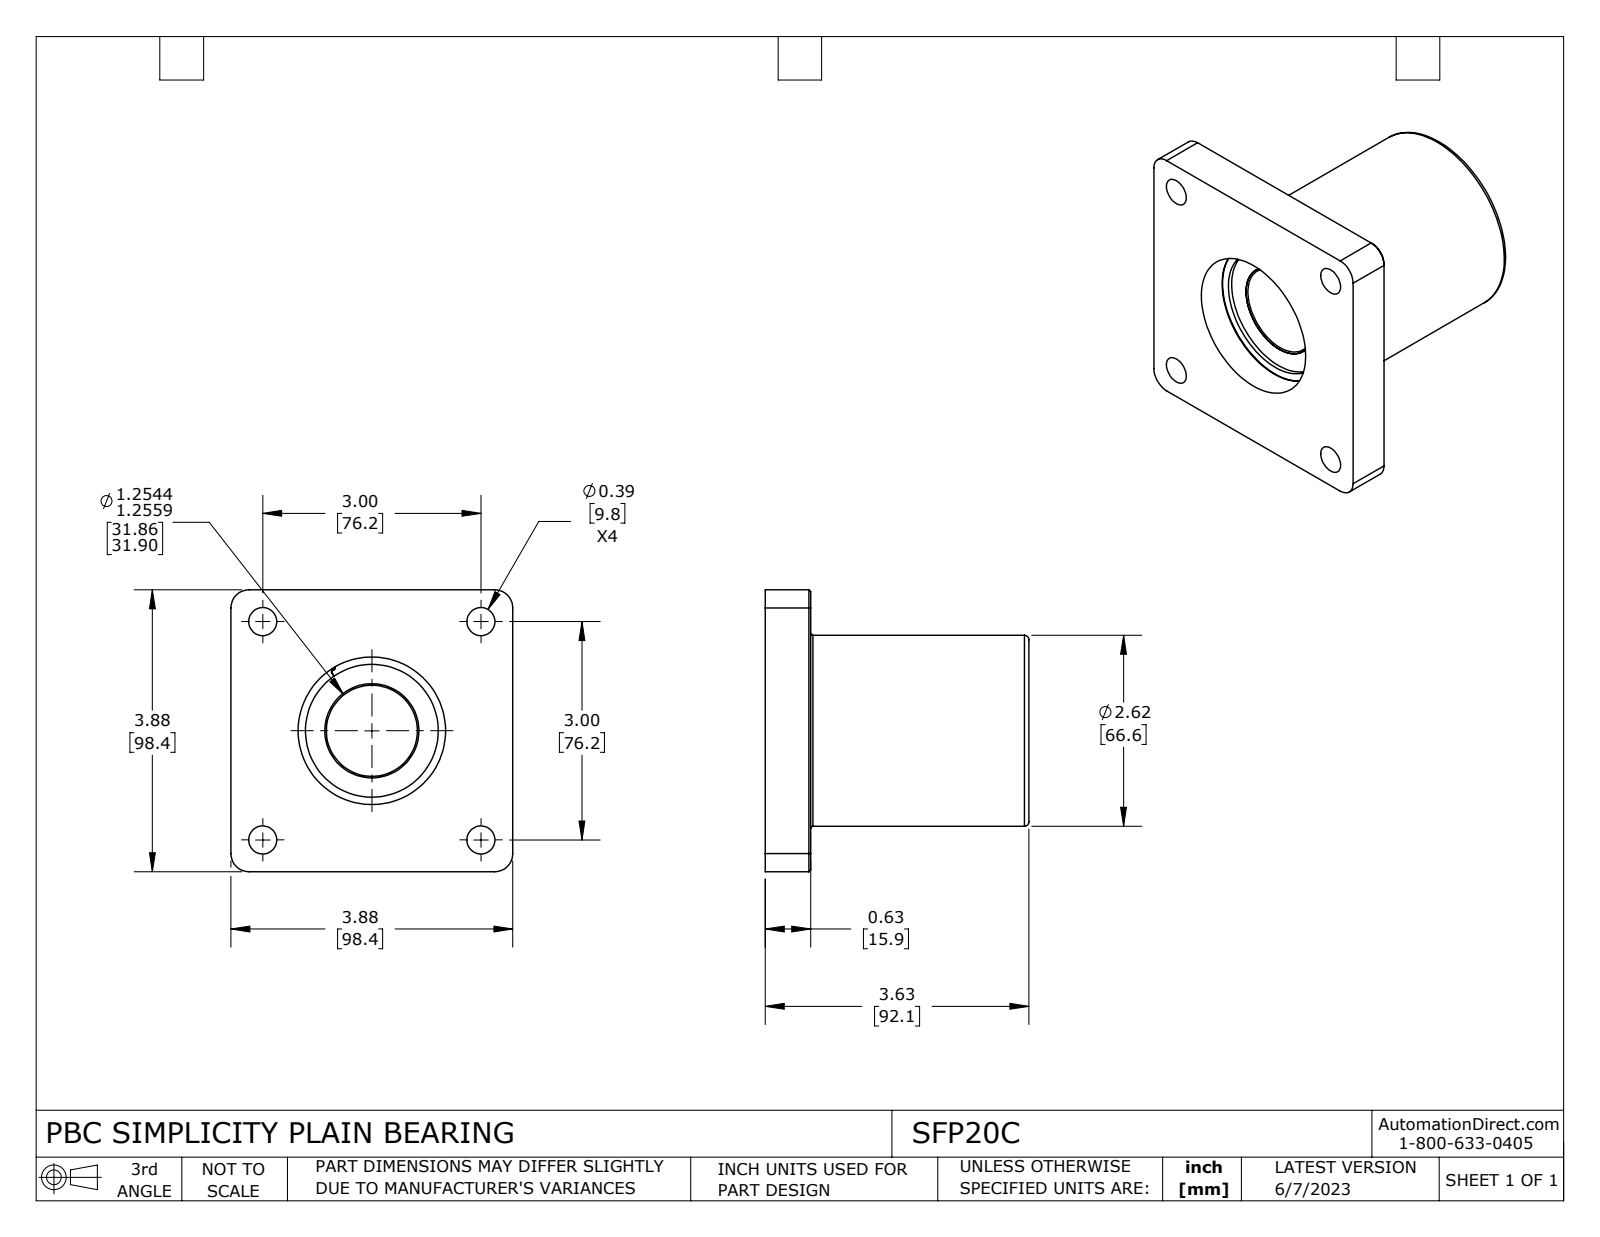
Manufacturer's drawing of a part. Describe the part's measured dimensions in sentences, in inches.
The part is named "SFP20C". Its 3-D file was written by "SolidWorks 2021 (CONFIG_CONTROL_DESIGN)". It is 7 solids with 169 faces: 41 planar, 74 cylindrical and 54 other. Overall it measures 3.875 by 3.875 by 3.625 inches. Its volume is 18.61 cubic inches and its surface area 147.2 square inches. Round holes: 4 of diameter 0.386, 1 of diameter 1.252, 1 of diameter 1.295, 1 of diameter 1.826, 1 of diameter 2.028, 1 of diameter 2.122. Round bosses or shafts: 1 of diameter 2.624, 1 of diameter 2.142, 1 of diameter 1.999, 1 of diameter 1.889, 1 of diameter 1.838. Partial cylindrical surfaces (rounded edges, fillets, slot ends): 4 of radius 0.026, 4 of radius 0.25, 2 of radius 0.021, 2 of radius 0.031. The main face-to-face distances are 0.625, 3.875, 0.488, 3.137, 0.503, 3.121, 0.122, 2.618, 2.496, 3.625. The hole center spacings are 2.121, 3, 4.243.
